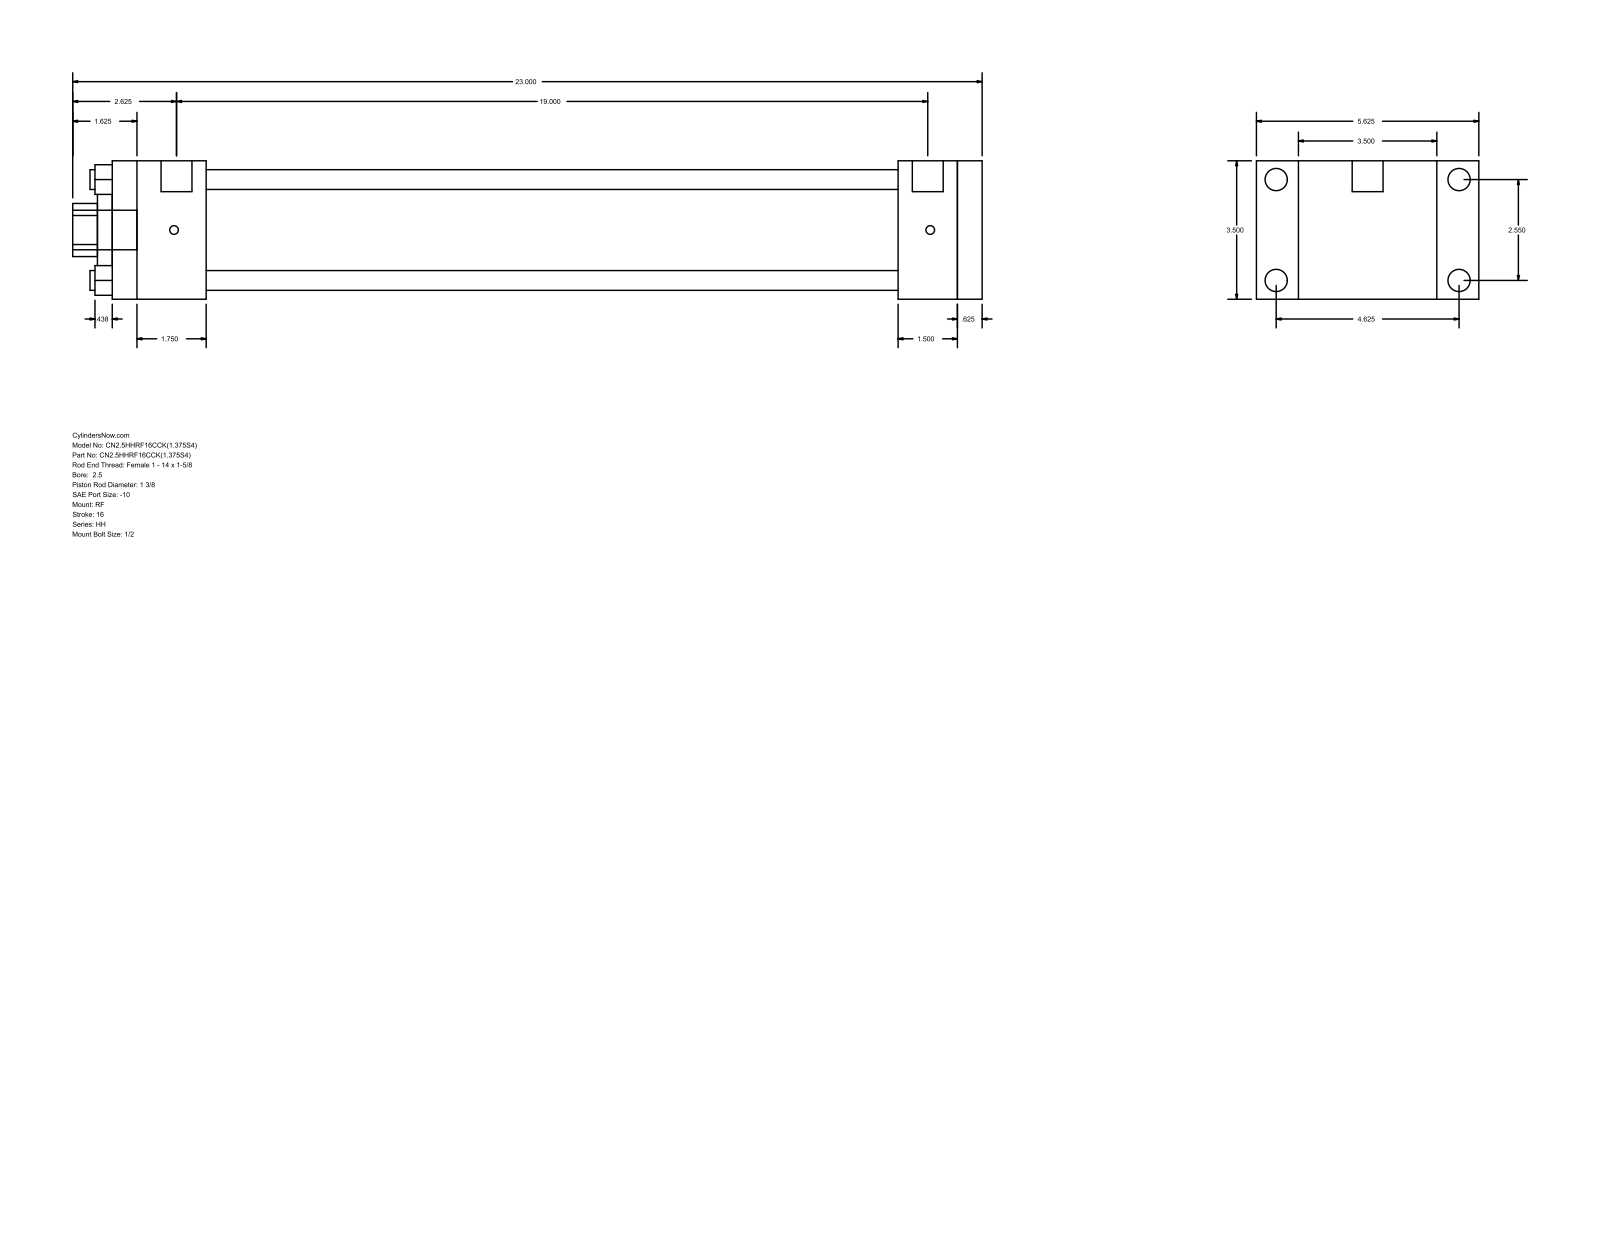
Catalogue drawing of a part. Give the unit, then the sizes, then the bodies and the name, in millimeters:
Units: millimetres
Overall size (bounding box): 584.2 × 142.88 × 88.9
Round holes (diameter × count): ⌀12.7 ×4, ⌀34.92 ×1, ⌀50.8 ×1, ⌀73.03 ×1
Round bosses / shafts (diameter × count): ⌀14.3 ×4, ⌀5.56 ×4, ⌀19.84 ×2, ⌀25.4 ×1
Partial cylindrical surfaces — rounded edges, fillets, slot ends (radius × count): R17.06 ×1
Main face-to-face distances: 88.9, 15.87, 542.93, 558.8, 60.32, 482.61, 498.48, 504.83, 444.51, 38.1
Hole centre spacings: 45.79, 64.76, 91.58
Bodies: 0 solids, 92 faces (64 planar, 28 cylindrical, 0 other)
Part name (STEP PRODUCT): HH_RF__0250_1.375
STEP written by: GSSL Pune (CONFIG_CONTROL_DESIGN)
